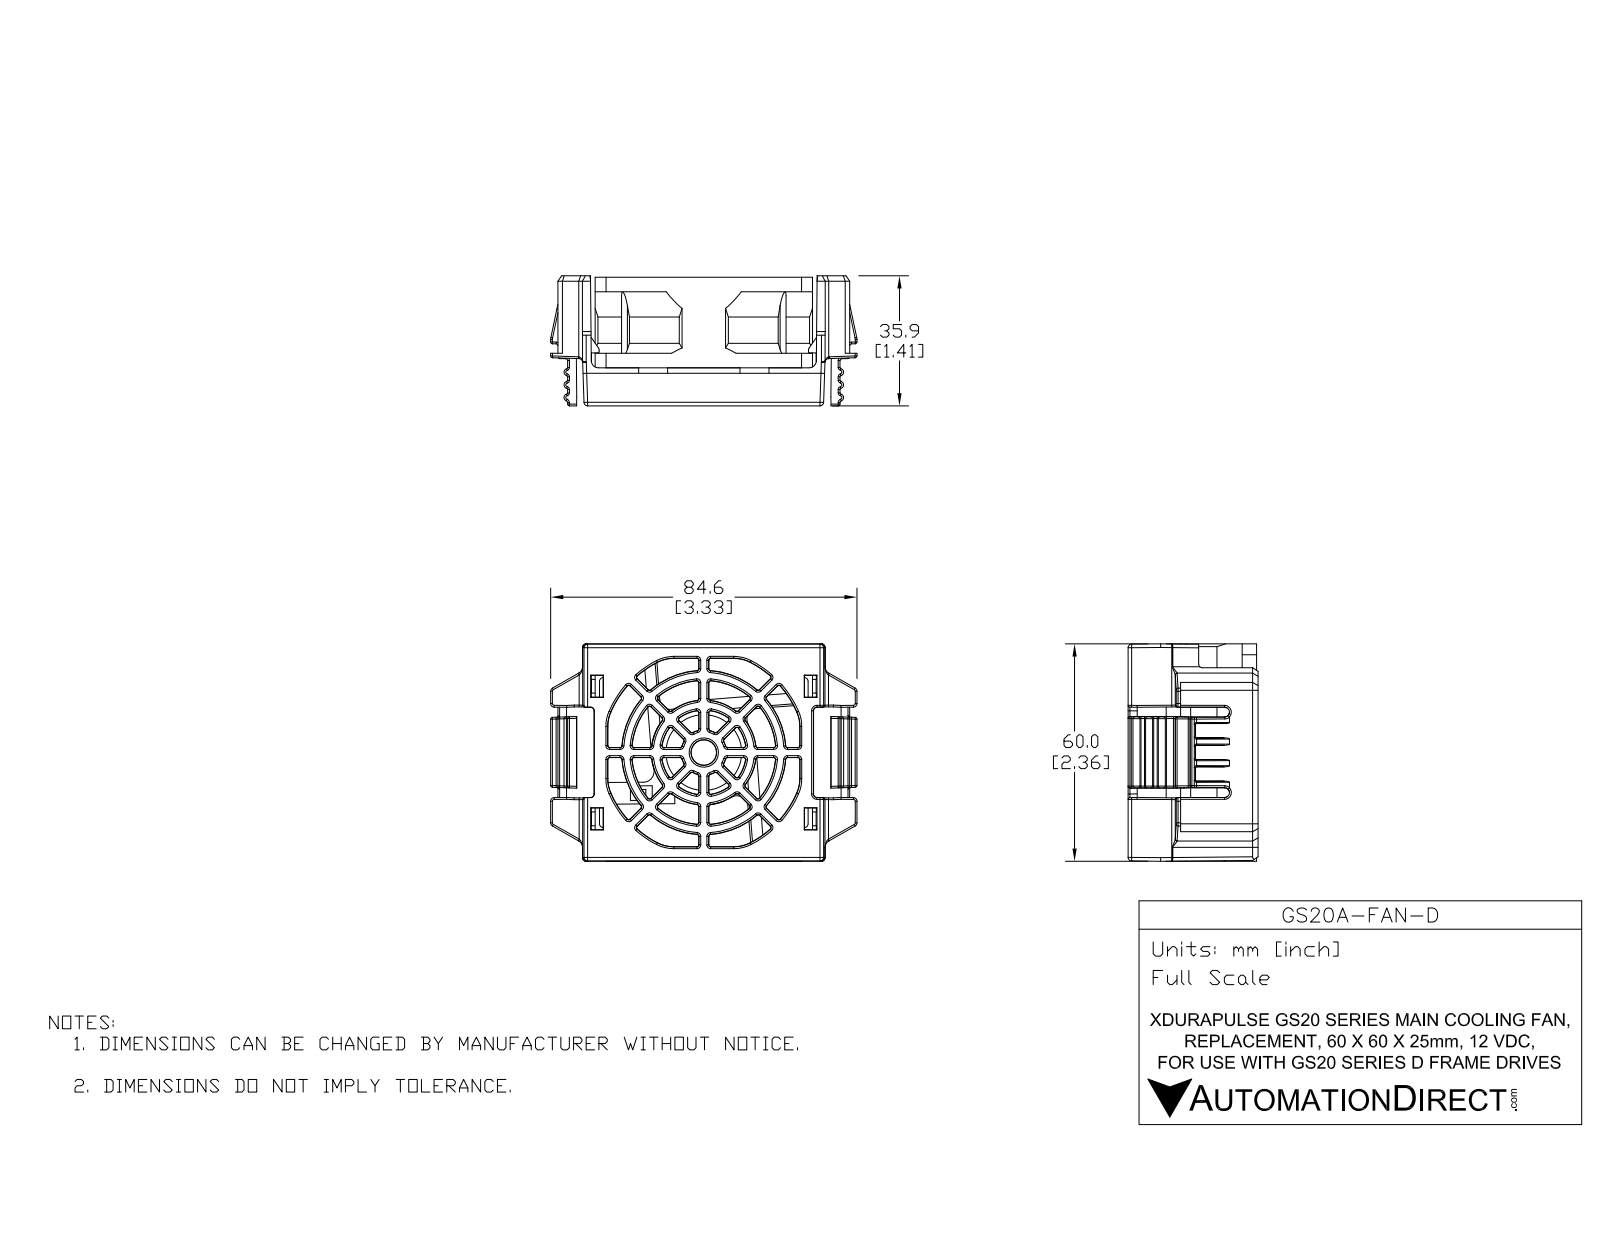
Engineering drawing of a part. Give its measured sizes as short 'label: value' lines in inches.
name: GS20A-FAN-D
written by: SolidWorks 2017 (AUTOMOTIVE_DESIGN)
unit: in
bodies: 2 solids, 1667 faces (509 planar, 397 cylindrical, 761 other)
size: 3.331 × 2.362 × 1.413
volume: 2.172 in³; area: 57.34 in²
holes: 4× ⌀0.169, 1× ⌀1.063, 1× ⌀2.268
bosses: 1× ⌀0.823
rounds: 110× R0.02, 51× R0.039, 38× R0.012, 10× R0.016, 10× R0.118, 6× R0.079, 6× R0.197, 4× R0.037
face distances: 0.098, 2.362, 0.047, 2.315, 1.299, 1.398, 0.827, 0.157, 0.406, 2.768
hole spacings: 1.392, 1.392, 1.968, 1.969, 2.783
